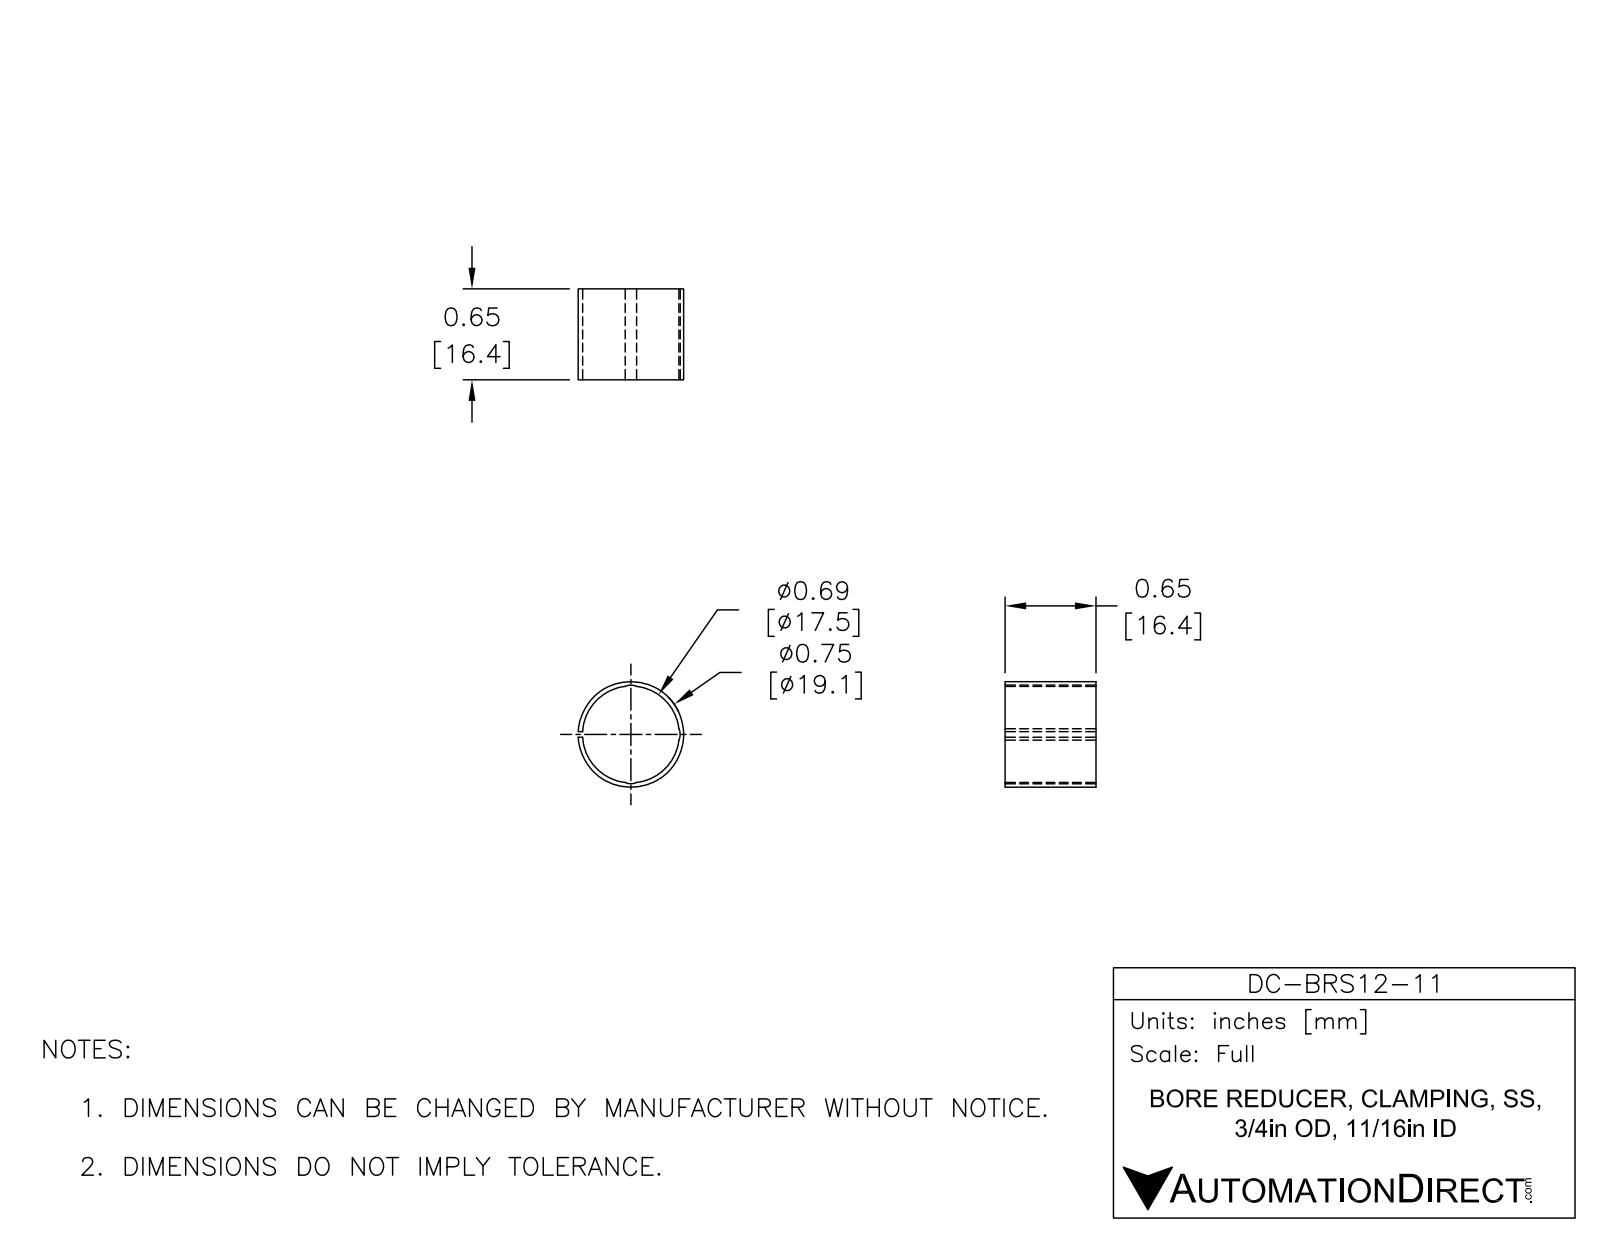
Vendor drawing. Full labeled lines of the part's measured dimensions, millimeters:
Part name (STEP PRODUCT): DC-BRS12-11
STEP written by: SolidWorks 2015 (AUTOMOTIVE_DESIGN)
Units: millimetres
Bodies: 1 solid, 15 faces (4 planar, 11 cylindrical, 0 other)
Overall size (bounding box): 19.05 × 19.04 × 16.41
Volume: 722 mm³ · Surface area: 1 966 mm²
Round holes (diameter × count): ⌀17.46 ×1
Round bosses / shafts (diameter × count): ⌀19.05 ×1
Partial cylindrical surfaces — rounded edges, fillets, slot ends (radius × count): R2.38 ×3
Main face-to-face distances: 16.4, 1.02
